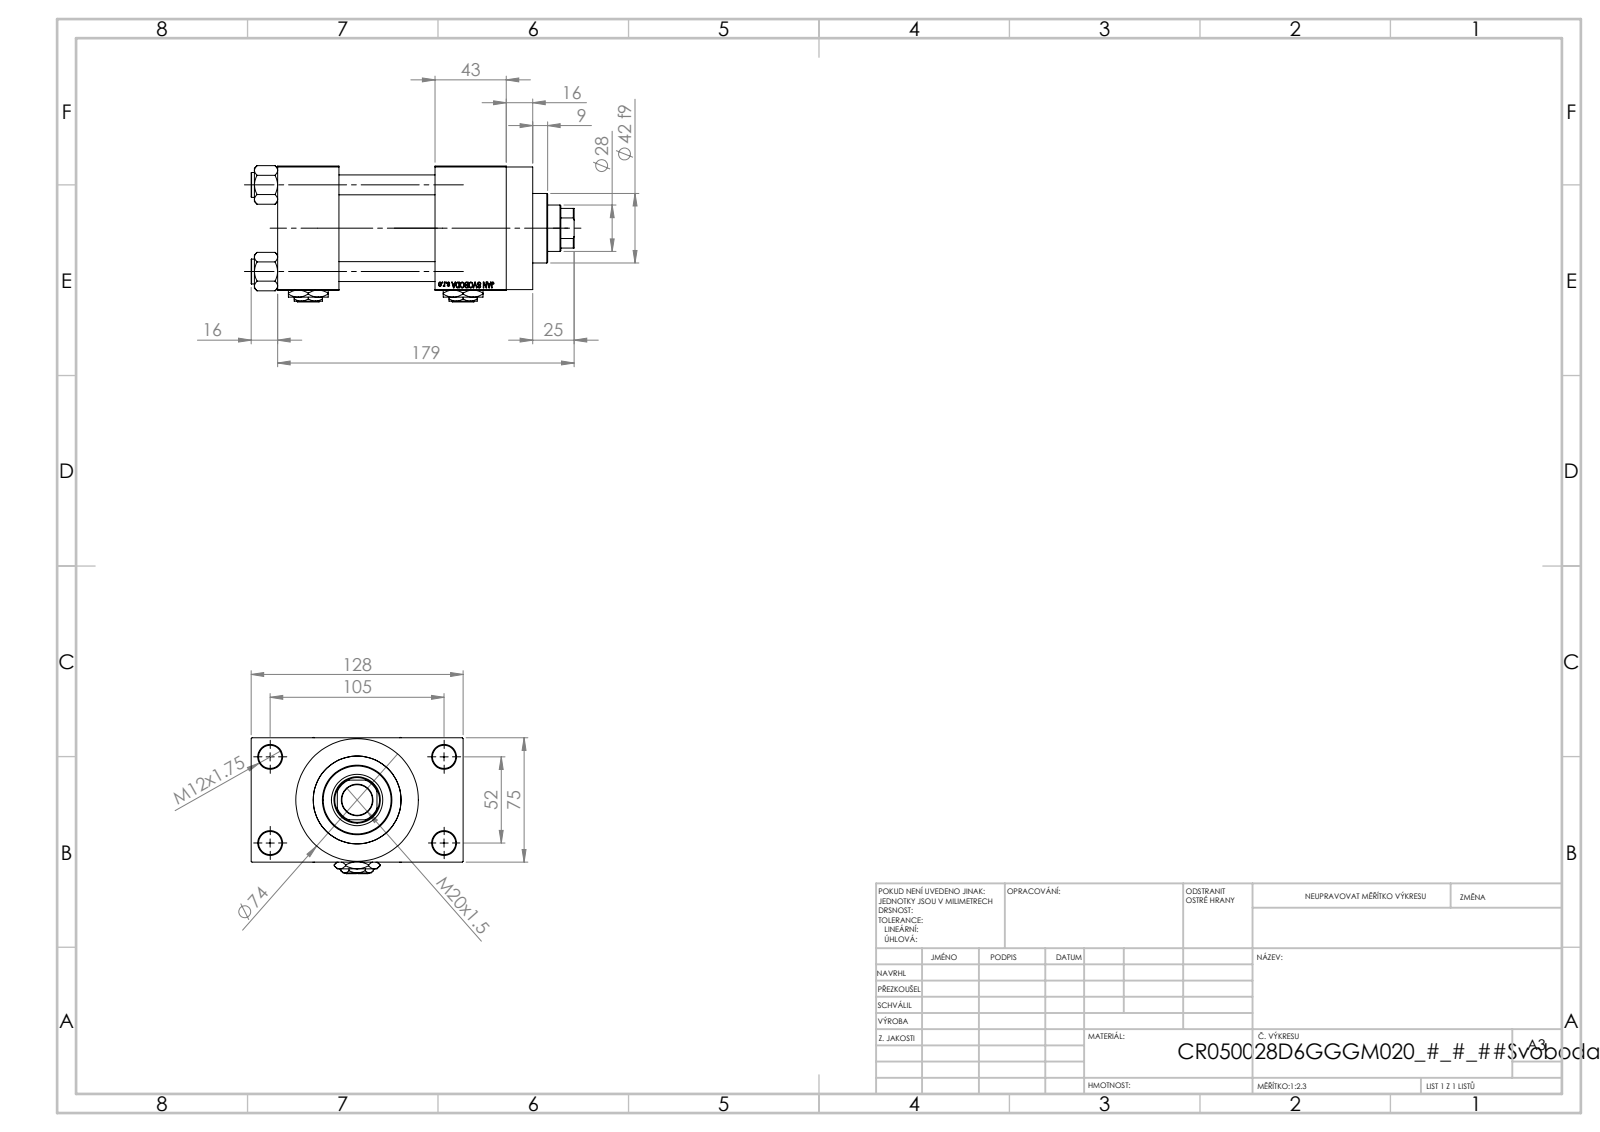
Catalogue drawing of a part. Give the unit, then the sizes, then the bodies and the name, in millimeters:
Units: millimetres
Overall size (bounding box): 195 × 128 × 82.27
Round holes (diameter × count): ⌀12 ×4, ⌀14 ×4, ⌀7 ×2, ⌀20.96 ×2, ⌀30 ×2, ⌀18.5 ×1, ⌀28 ×1, ⌀31 ×1, ⌀41 ×1, ⌀50 ×1, ⌀53 ×1
Round bosses / shafts (diameter × count): ⌀15 ×4, ⌀74 ×1, ⌀56 ×1, ⌀42 ×1
Partial cylindrical surfaces — rounded edges, fillets, slot ends (radius × count): R13.5 ×1
Main face-to-face distances: 75, 58, 37, 95, 101.5, 26.5, 138, 101, 43, 16
Hole centre spacings: 26.35, 36.98, 52.3, 58.43, 58.59, 78.65, 94.37, 52
Volume: 810 868 mm³ · Surface area: 173 104 mm²
Bodies: 13 solids, 1205 faces (545 planar, 100 cylindrical, 560 other)
Part name (STEP PRODUCT): V215CR_D_TYCINKA; V215CR_VCP_D; V215CR_D_Body; NUT_M5_D (+2 more)
STEP written by: SolidWorks 2019 (CONFIG_CONTROL_DESIGN)
